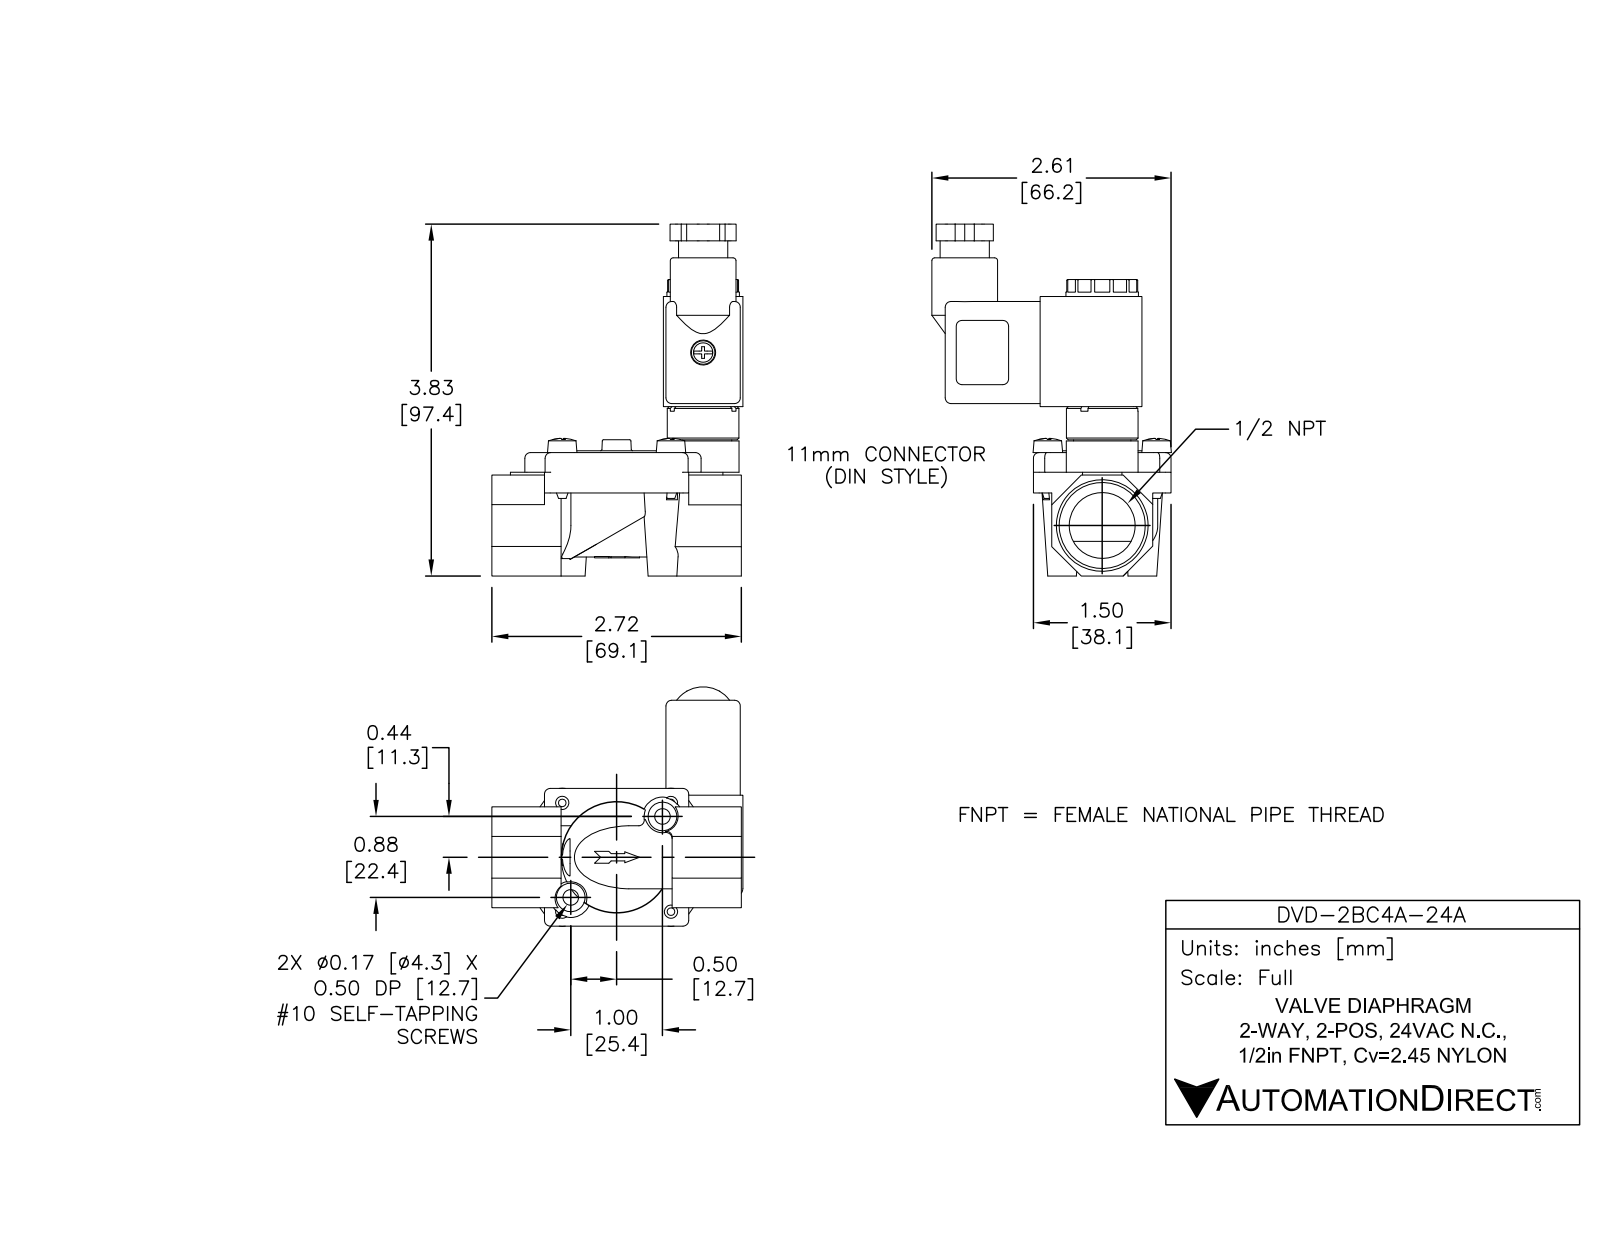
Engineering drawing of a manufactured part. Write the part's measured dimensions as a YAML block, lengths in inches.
part_name: "DVD-2BC4A-24A"
step_written_by: "SolidWorks 2015 (AUTOMOTIVE_DESIGN)"
units: inches
bodies: {solids: 13, faces: 1449, planar: 725, cylindrical: 257, other: 467}
overall_size: [3.834, 2.736, 2.611]
volume: 3.855
surface_area: 61.59
round_holes:
  - {diameter: 0.144, count: 4}
  - {diameter: 0.164, count: 4}
  - {diameter: 0.06, count: 2}
  - {diameter: 0.093, count: 2}
  - {diameter: 0.17, count: 2}
  - {diameter: 0.703, count: 2}
  - {diameter: 0.062, count: 1}
  - {diameter: 0.156, count: 1}
  - {diameter: 0.166, count: 1}
  - {diameter: 0.25, count: 1}
  - {diameter: 0.272, count: 1}
  - {diameter: 0.312, count: 1}
round_bosses_or_shafts:
  - {diameter: 0.187, count: 4}
  - {diameter: 0.125, count: 4}
  - {diameter: 0.625, count: 2}
  - {diameter: 1.375, count: 1}
  - {diameter: 0.79, count: 1}
  - {diameter: 0.782, count: 1}
  - {diameter: 0.781, count: 1}
  - {diameter: 0.716, count: 1}
partial_cylinders:
  - {radius: 0.01, count: 24}
  - {radius: 0.062, count: 24}
  - {radius: 0.156, count: 12}
  - {radius: 0.044, count: 3}
  - {radius: 0.094, count: 2}
  - {radius: 0.215, count: 2}
  - {radius: 0.314, count: 1}
  - {radius: 0.344, count: 1}
face_to_face_distances: [0.05, 1.1, 0.866, 0.76, 0.2, 1.3, 0.788, 0.078, 0.078, 0.71]
hole_center_spacings: [0.838, 1.185, 0.181, 0.664, 0.688, 1.034, 1.104, 1.502]
